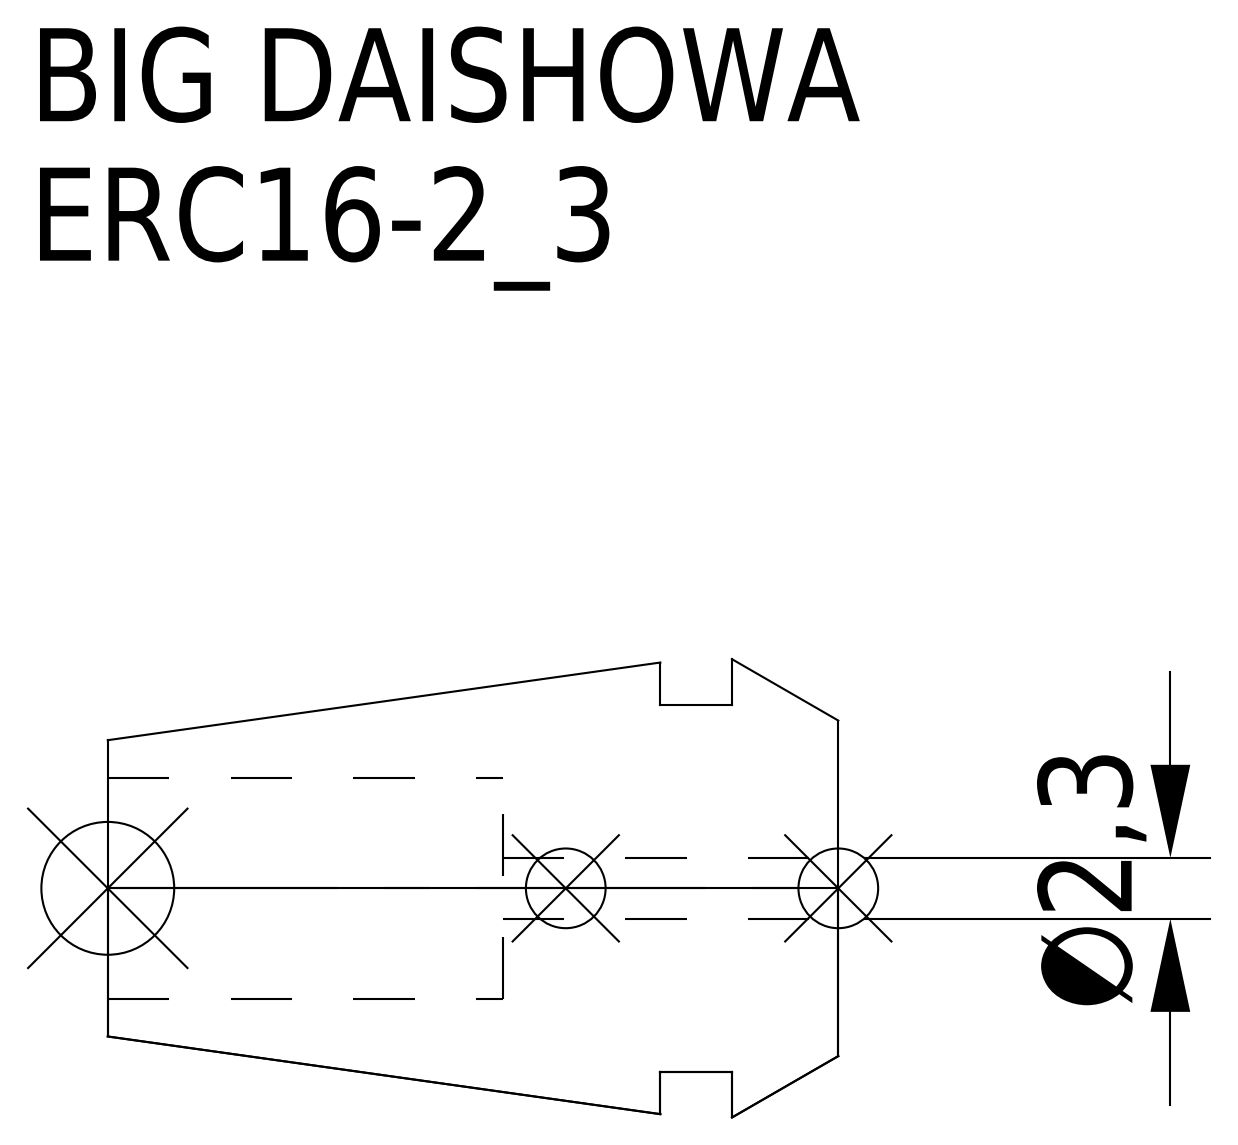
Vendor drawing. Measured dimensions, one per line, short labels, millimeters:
name: ERC16-2_3
written by: CREO PARAMETRIC BY PTC INC, 2016380 (AUTOMOTIVE_DESIGN)
unit: mm
bodies: 1 solid, 15 faces (5 planar, 6 cylindrical, 4 other)
size: 27.5 × 17.25 × 17.25
volume: 3 538 mm³; area: 2 118 mm²
holes: 1× ⌀2.3, 1× ⌀8.3
bosses: 1× ⌀13.8
face distances: 4, 6.7, 2.7, 12.63, 8.63, 5.93, 27.5, 23.5, 20.8, 14.87
